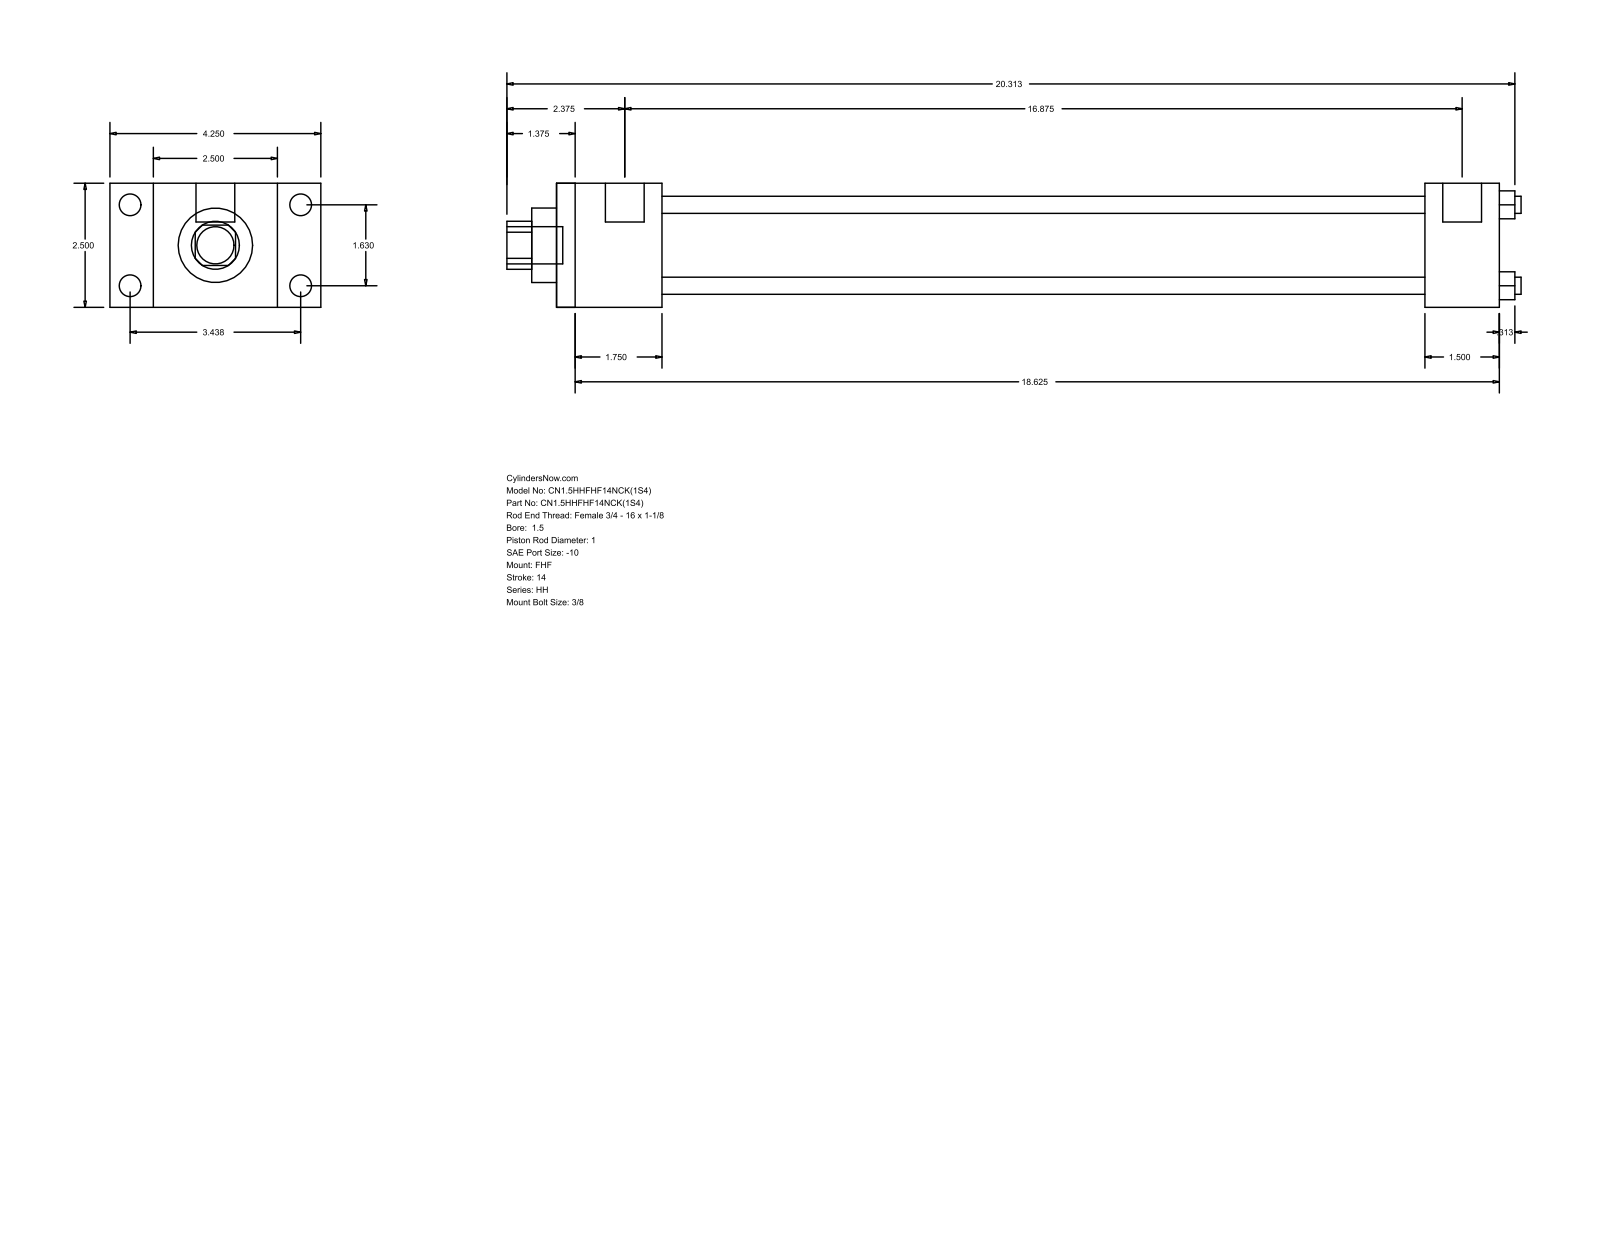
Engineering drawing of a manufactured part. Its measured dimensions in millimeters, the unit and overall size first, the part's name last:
Units: millimetres
Overall size (bounding box): 519.11 × 107.95 × 63.5
Round holes (diameter × count): ⌀8.76 ×4, ⌀25.4 ×1, ⌀38.1 ×1, ⌀44.45 ×1
Round bosses / shafts (diameter × count): ⌀11.13 ×4, ⌀5.56 ×4, ⌀19.84 ×2, ⌀19.05 ×1
Partial cylindrical surfaces — rounded edges, fillets, slot ends (radius × count): R12.29 ×1
Main face-to-face distances: 63.5, 22.23, 85.73, 53.98, 107.96, 482.6, 428.62, 444.5, 390.52, 38.1
Hole centre spacings: 29.27, 41.4, 58.55
Bodies: 0 solids, 88 faces (60 planar, 28 cylindrical, 0 other)
Part name (STEP PRODUCT): HH_FHF__0150_1
STEP written by: GSSL Pune (CONFIG_CONTROL_DESIGN)
